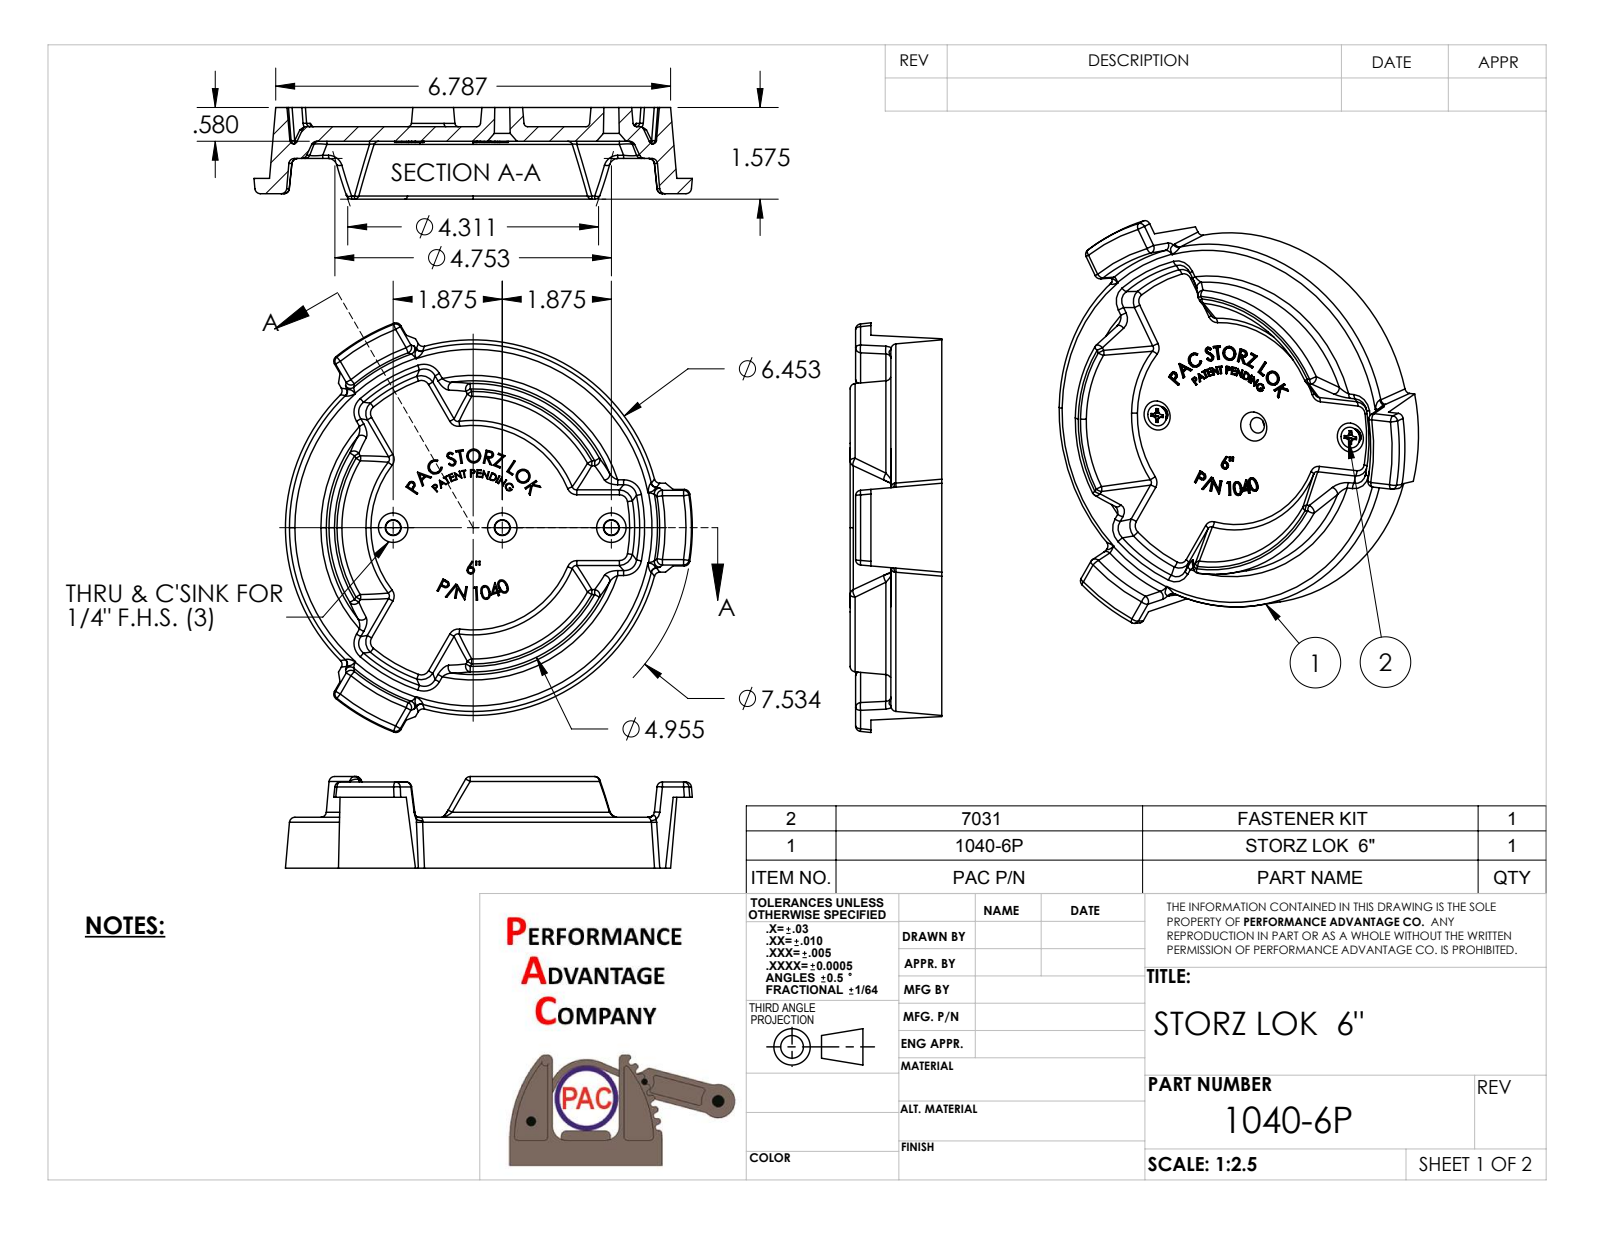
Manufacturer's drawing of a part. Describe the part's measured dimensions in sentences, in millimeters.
The part is named "1040-6". Its 3-D file was written by "SolidWorks 2010 (CONFIG_CONTROL_DESIGN)". It is 1 solid with 817 faces: 324 planar, 48 cylindrical and 445 other. Overall it measures 178.8 by 177.6 by 40 millimeters. Its volume is 253 500 cubic millimeters and its surface area 81 810 square millimeters. Partial cylindrical surfaces (rounded edges, fillets, slot ends): 30 of radius 2.4, 11 of radius 1.6, 7 of radius 1.6. The main face-to-face distances are 6.4, 7.5, 8.4, 14.7, 22.2, 13.8, 15.9, 1.1, 37.6, 29.2.
